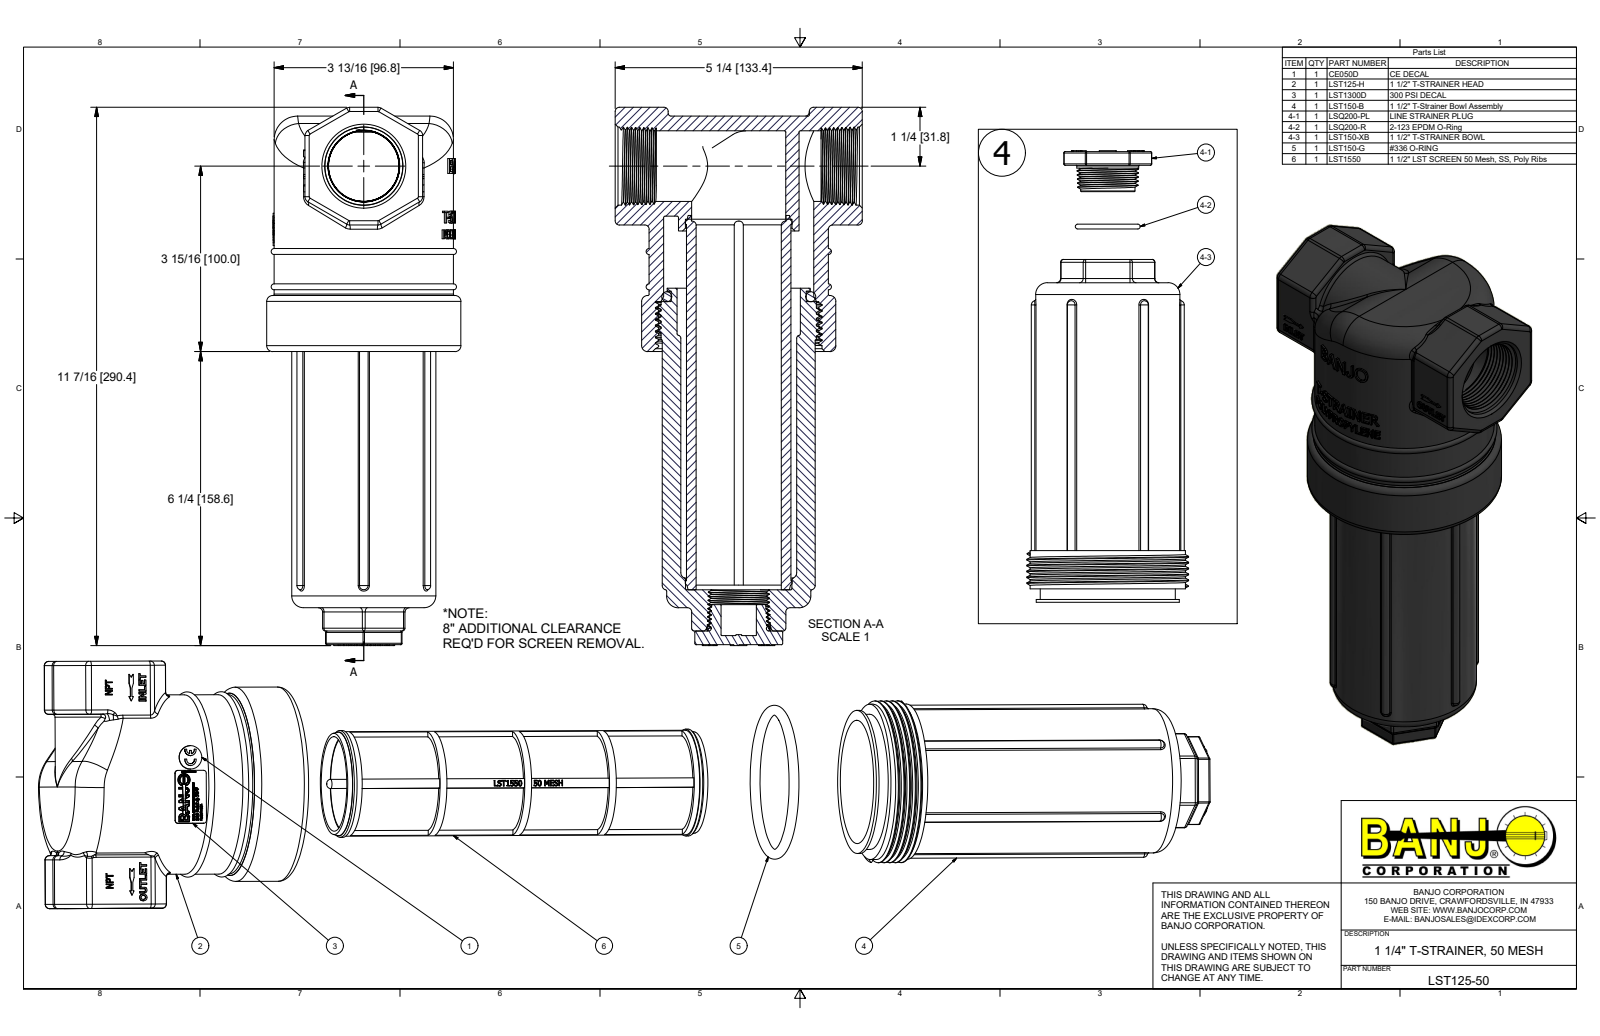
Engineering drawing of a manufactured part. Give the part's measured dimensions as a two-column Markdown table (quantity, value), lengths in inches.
| quantity | value |
| --- | --- |
| part name | LST125-50; CE050D; LST125-H; LST1300D (+6 more) |
| STEP written by | Autodesk Inventor 2018 (AUTOMOTIVE_DESIGN) |
| units | inches |
| bodies | 8 solids, 3124 faces (1688 planar, 298 cylindrical, 1138 other) |
| overall size | 48.286 × 11.433 × 4.125 |
| volume | 50.28 in³ |
| surface area | 752.8 in² |
| round holes (diameter × count) | 0.181 × 1, 0.257 × 1, 0.75 × 1, 1.5 × 1, 1.81 × 1, 1.97 × 1, 2 × 1, 2.26 × 1, 2.265 × 1, 2.62 × 1, 3.19 × 1, 3.403 × 1 |
| round bosses / shafts (diameter × count) | 4.125 × 1, 3.81 × 1, 3.435 × 1, 3.3 × 1, 3.063 × 1, 3.04 × 1, 2.87 × 1, 2.563 × 1 |
| partial cylindrical surfaces (radius × count) | 0.03 × 44, 0.09 × 34, 0.06 × 16, 0.125 × 10, 0.078 × 6, 0.094 × 6, 0.1 × 4, 0.026 × 2 |
| main face-to-face distances | 2.5, 10.06, 6.12, 3.94, 0.92, 1.24, 9.748, 3.628, 0.313, 5.25 |
